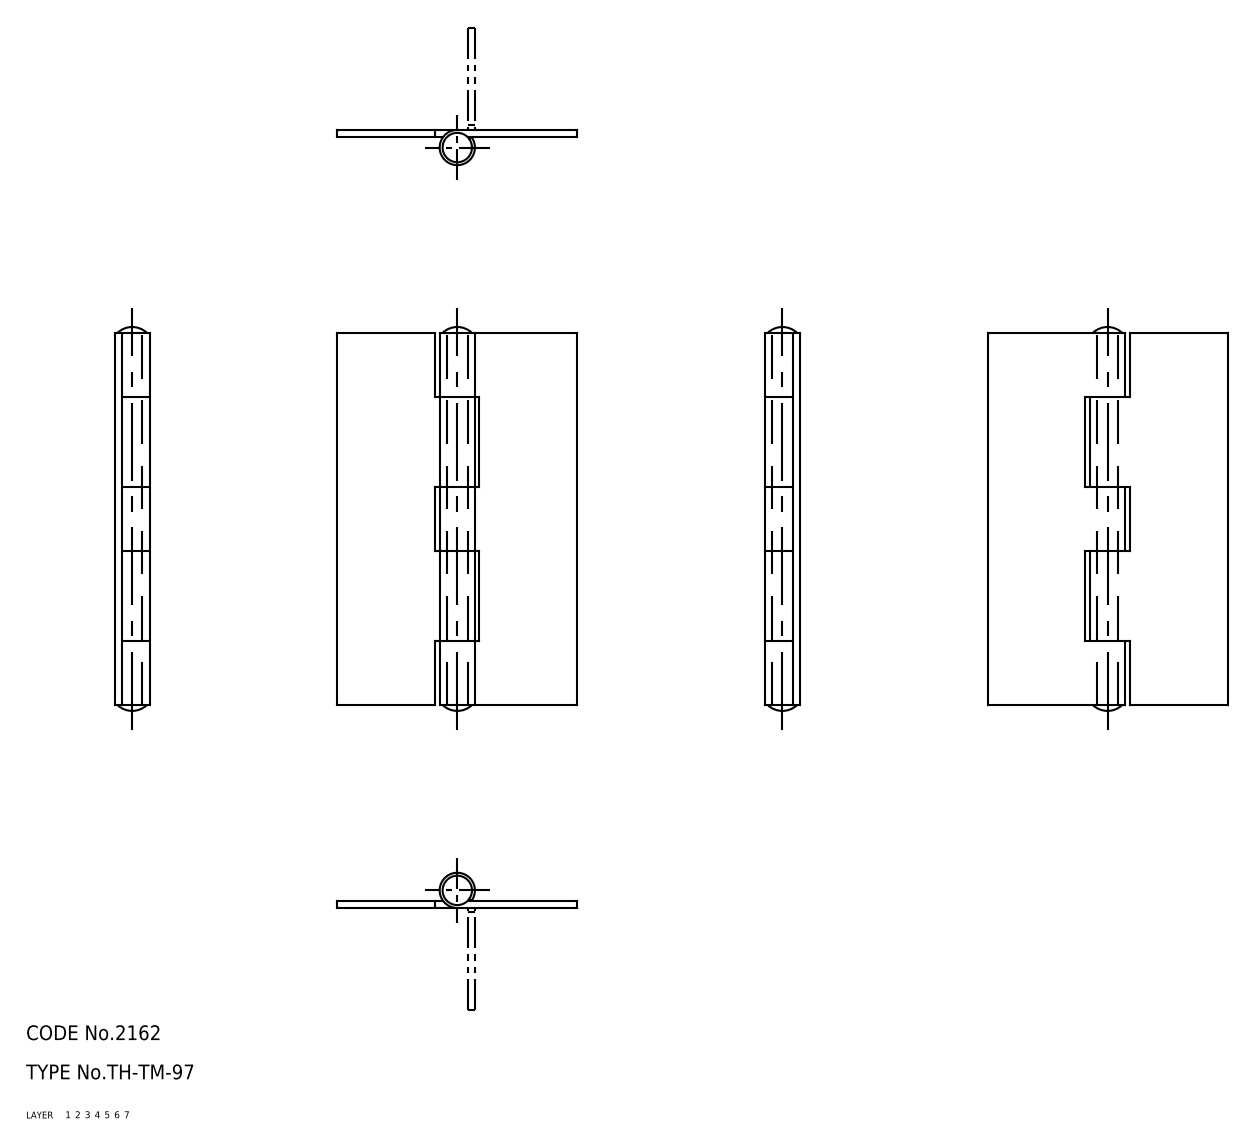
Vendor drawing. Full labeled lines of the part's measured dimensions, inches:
Part name (STEP PRODUCT): 67111002; 67111015; 67111028
STEP written by: CADfix (AUTOMOTIVE_DESIGN)
Units: inches
Bodies: 3 solids, 44 faces (0 planar, 0 cylindrical, 44 other)
Overall size (bounding box): 3.087 × 1.929 × 0.283
Volume: 0.482 in³ · Surface area: 17.11 in²
